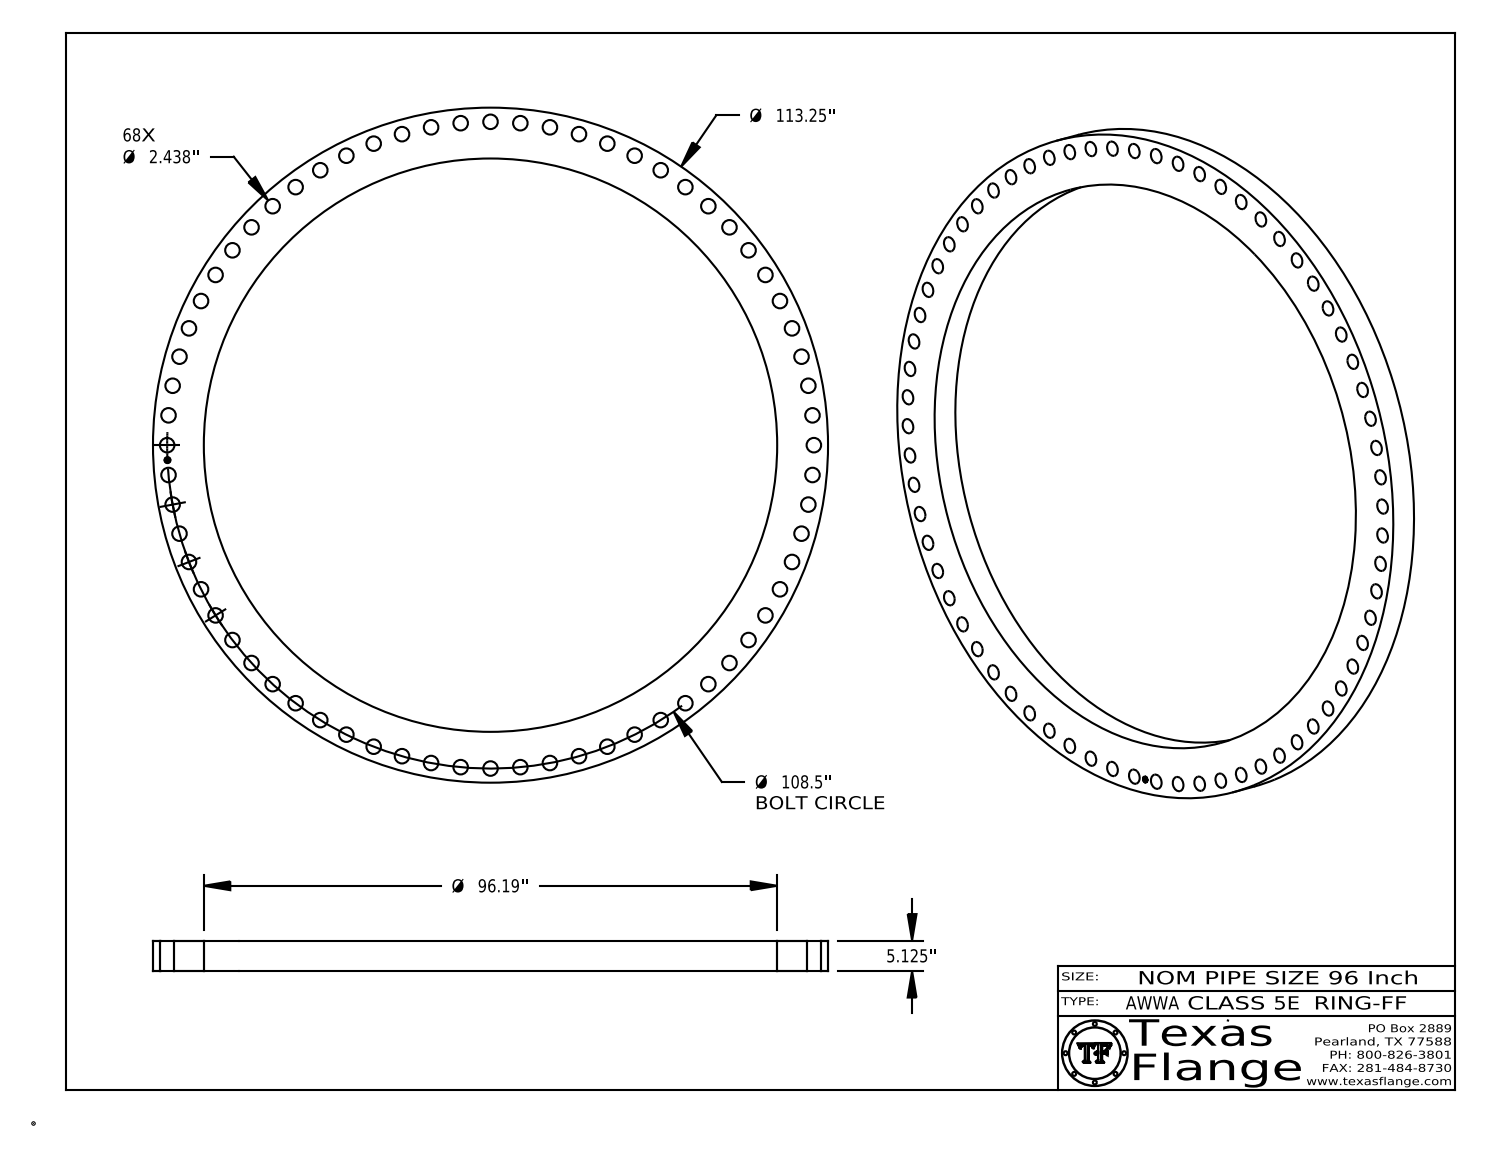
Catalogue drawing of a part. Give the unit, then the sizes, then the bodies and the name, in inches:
Units: inches
Overall size (bounding box): 113.25 × 113.25 × 5.125
Round holes (diameter × count): ⌀2.438 ×68, ⌀1 ×1, ⌀96.19 ×1
Round bosses / shafts (diameter × count): ⌀0.061 ×8, ⌀113.25 ×1, ⌀0.788 ×1
Main face-to-face distances: 5.125, 0.015, 5.11, 0.298, 0.293, 0.054, 0.193, 0.248, 0.044, 0.15
Hole centre spacings: 54.25, 29.693, 5.011, 10.011, 14.99, 19.937, 39.195, 43.826
Volume: 12 755 in³ · Surface area: 11 019 in²
Bodies: 1 solid, 527 faces (367 planar, 160 cylindrical, 0 other)
Part name (STEP PRODUCT): AWWA Class 5E-RING-FF
STEP written by: CATIA V5 STEP AP214 (AUTOMOTIVE_DESIGN)
